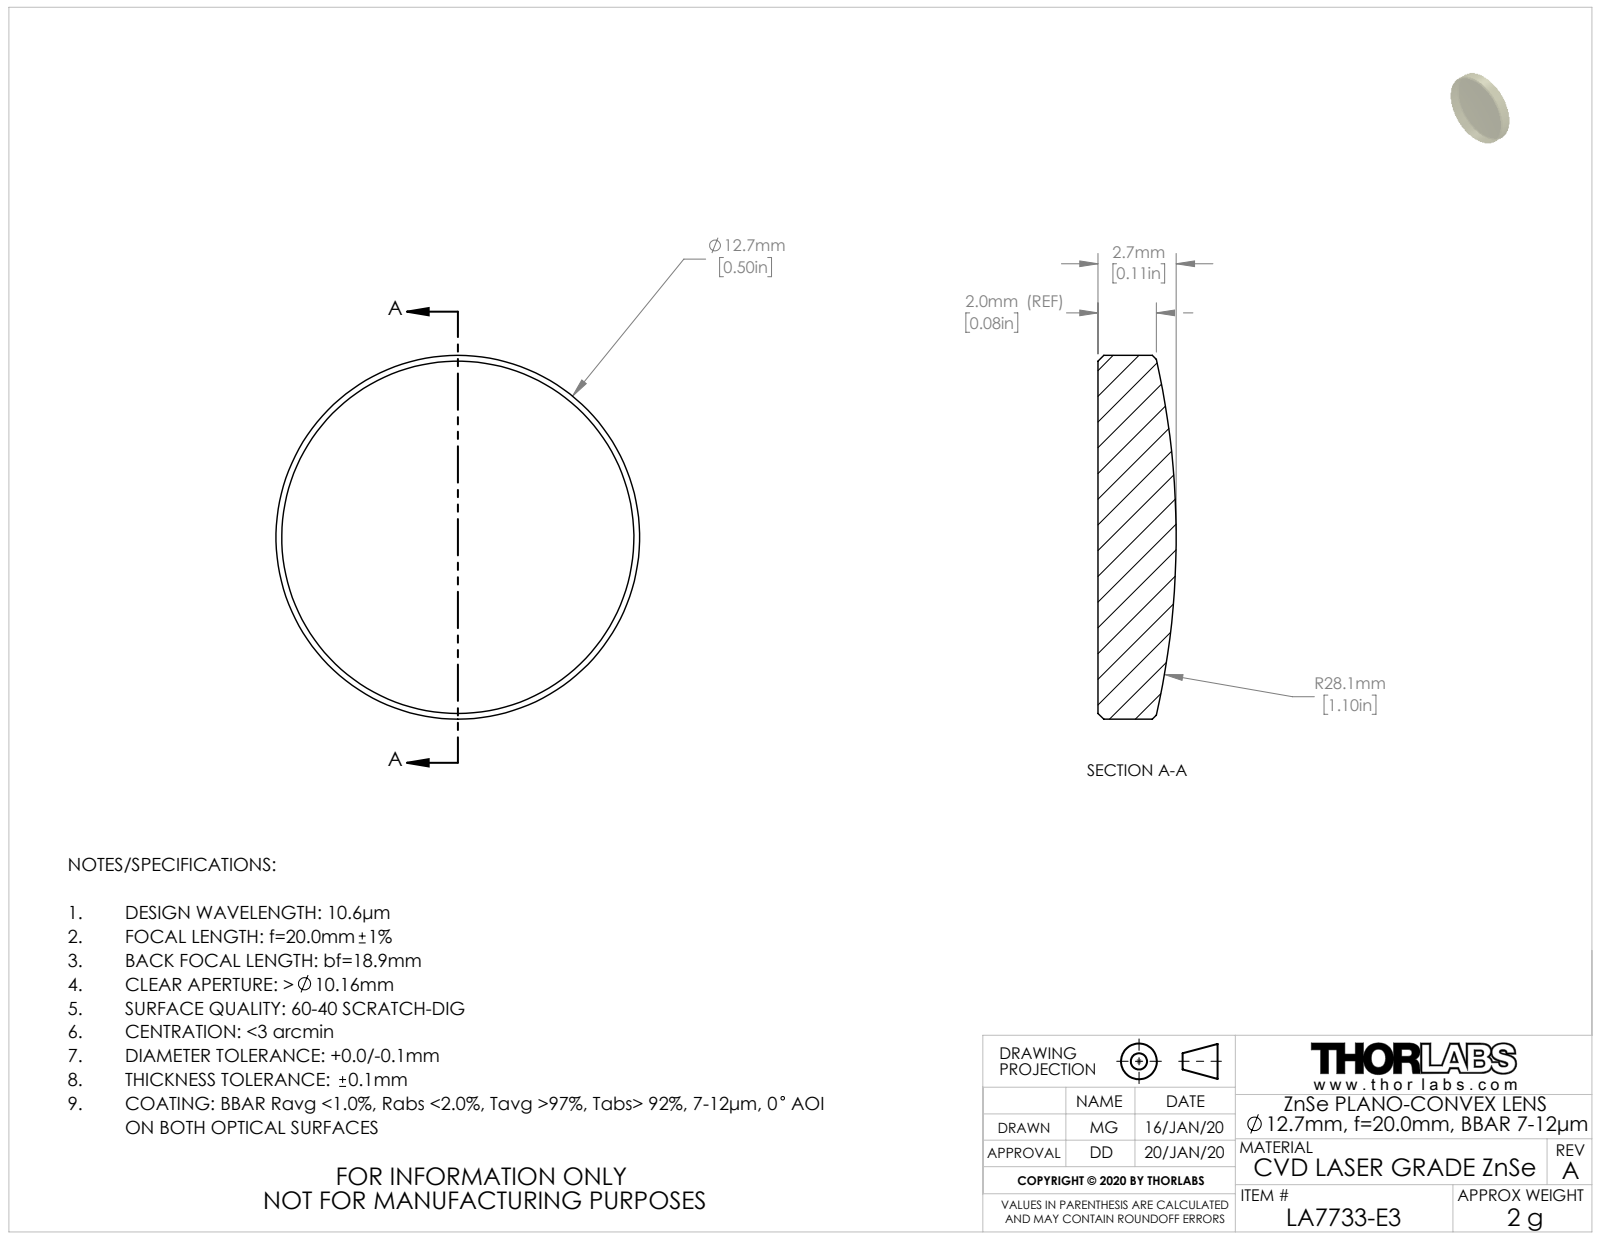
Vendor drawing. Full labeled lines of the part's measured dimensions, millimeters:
Part name (STEP PRODUCT): TTN206020-E0W
STEP written by: SolidWorks 2018 (CONFIG_CONTROL_DESIGN)
Units: millimetres
Bodies: 1 solid, 9 faces (1 planar, 2 cylindrical, 6 other)
Overall size (bounding box): 12.7 × 12.7 × 2.73
Volume: 299 mm³ · Surface area: 328 mm²
Round bosses / shafts (diameter × count): ⌀12.7 ×1
